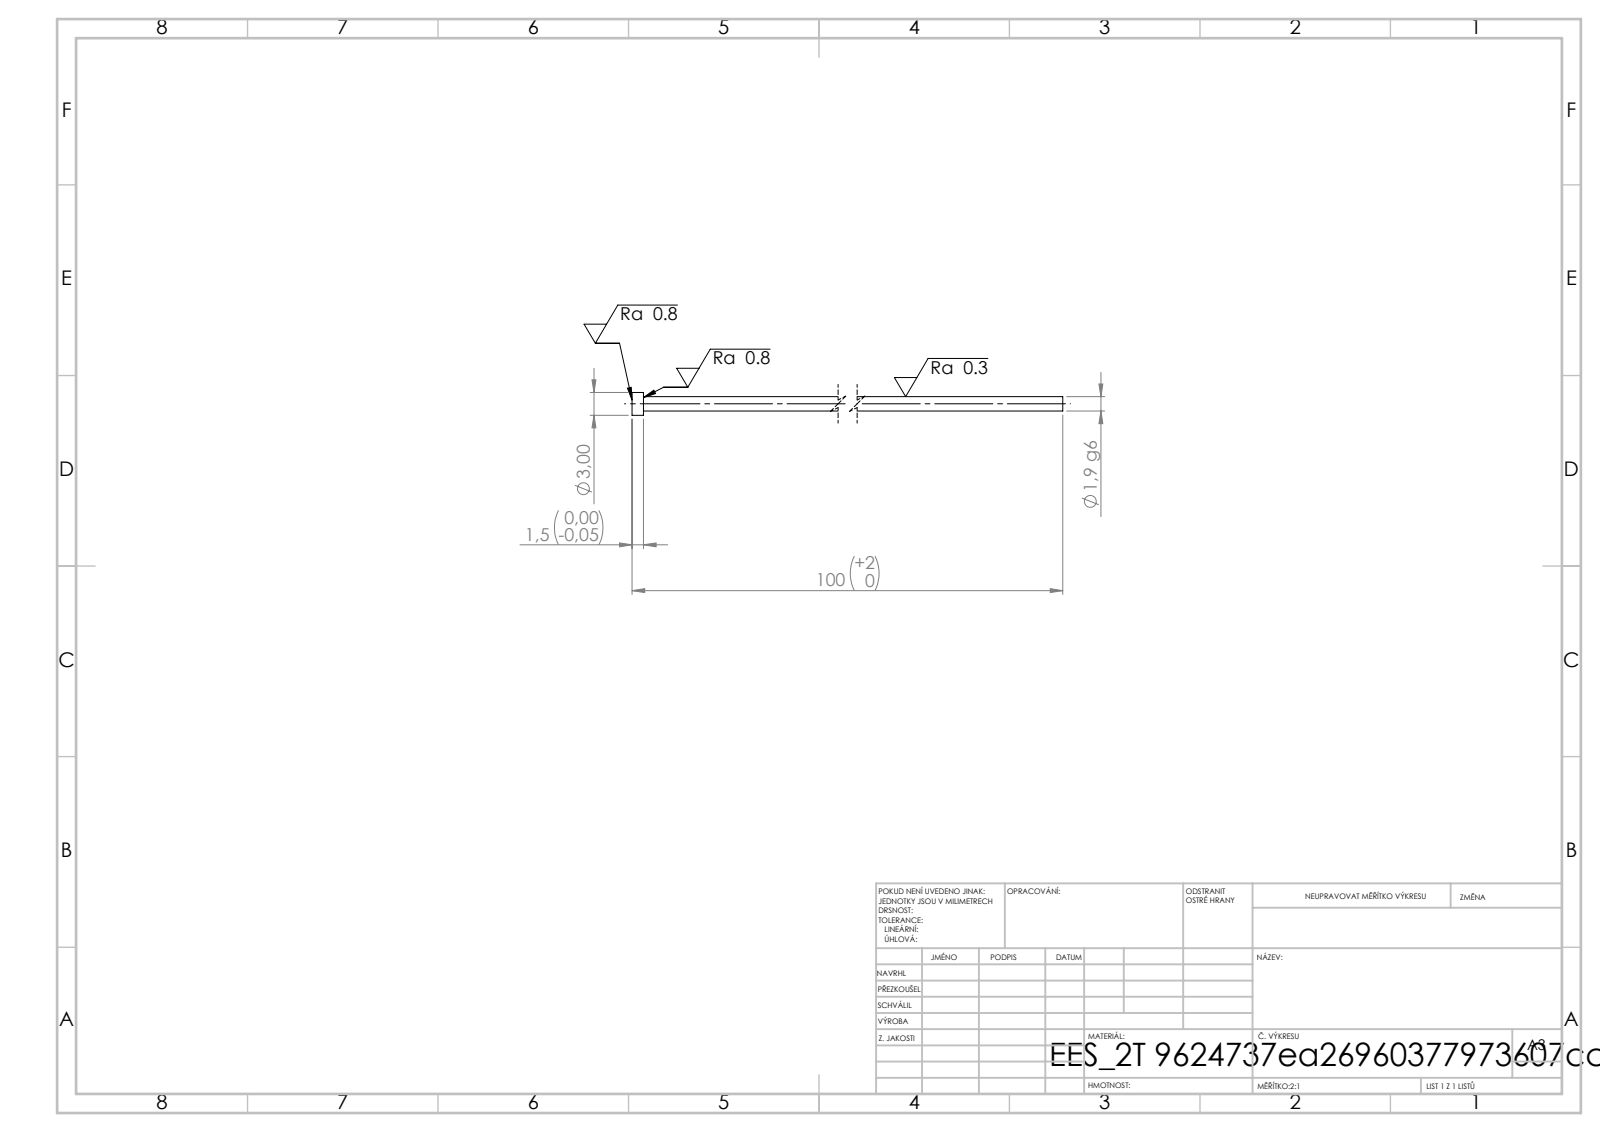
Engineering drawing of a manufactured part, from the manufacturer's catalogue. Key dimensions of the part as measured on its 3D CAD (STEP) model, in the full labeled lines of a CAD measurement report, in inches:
STEP written by: SolidWorks 2019 (CONFIG_CONTROL_DESIGN)
Units: inches
Bodies: 1 solid, 7 faces (3 planar, 4 cylindrical, 0 other)
Overall size (bounding box): 3.937 × 0.118 × 0.118
Volume: 0.018 in³ · Surface area: 0.955 in²
Round bosses / shafts (diameter × count): ⌀0.118 ×1, ⌀0.075 ×1
Main face-to-face distances: 0.059, 3.937, 3.878
